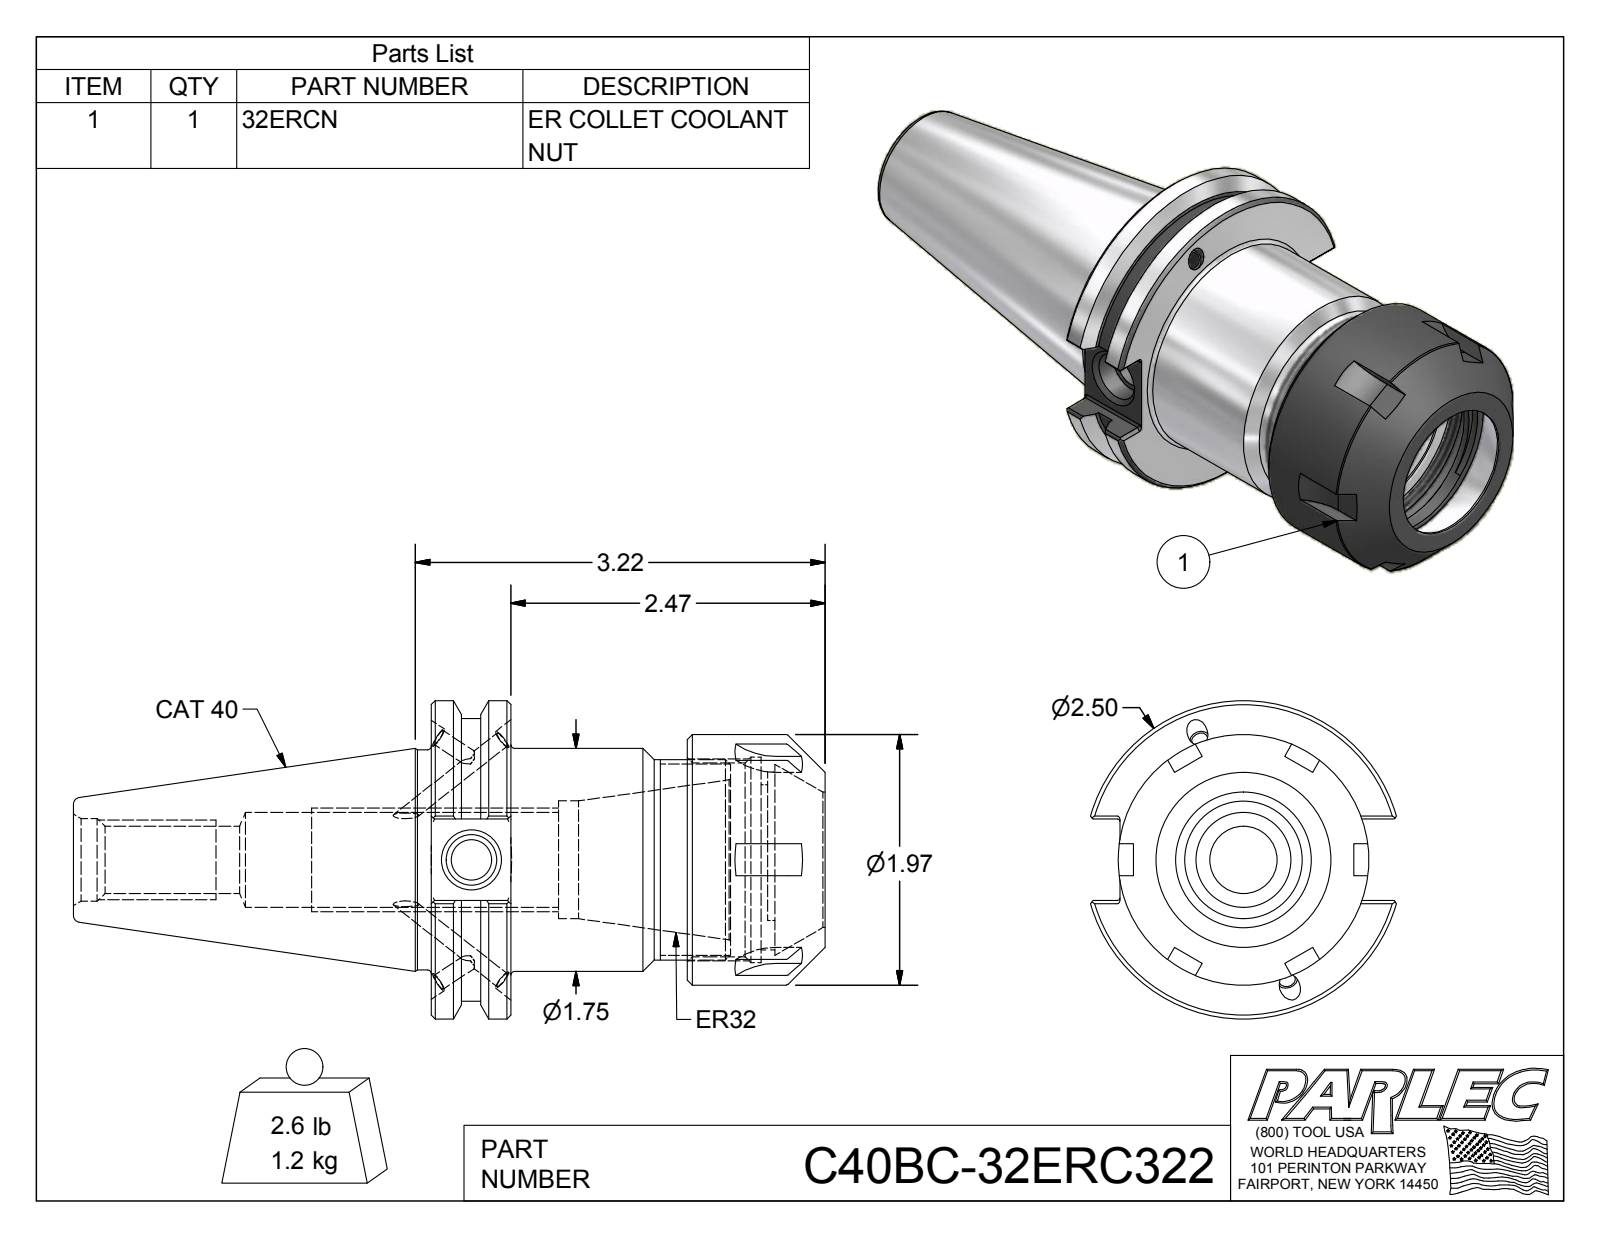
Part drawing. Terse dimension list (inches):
name: C40BC-32ERC322; C40BC-32ER3-1; 32ERCN
written by: Autodesk Inventor 2012 (AUTOMOTIVE_DESIGN)
unit: in
bodies: 2 solids, 143 faces (59 planar, 47 cylindrical, 37 other)
size: 5.908 × 2.5 × 2.403
volume: 9.32 in³; area: 62.68 in²
holes: 4× ⌀0.13, 4× ⌀0.161, 1× ⌀0.315, 1× ⌀0.399, 1× ⌀0.527, 1× ⌀0.648, 1× ⌀0.745, 1× ⌀0.925, 1× ⌀1.063, 1× ⌀1.299, 1× ⌀1.522, 1× ⌀1.614
bosses: 1× ⌀2.5, 1× ⌀2.219, 1× ⌀1.969, 1× ⌀1.75, 1× ⌀1.73, 1× ⌀1.575
rounds: 12× R0.02, 6× R0.5, 1× R0.689
face distances: 0.625, 2.012, 1.387, 2.591, 1.966, 0.579, 3.095, 2.47, 1.083, 0.504
hole spacings: 0.059
